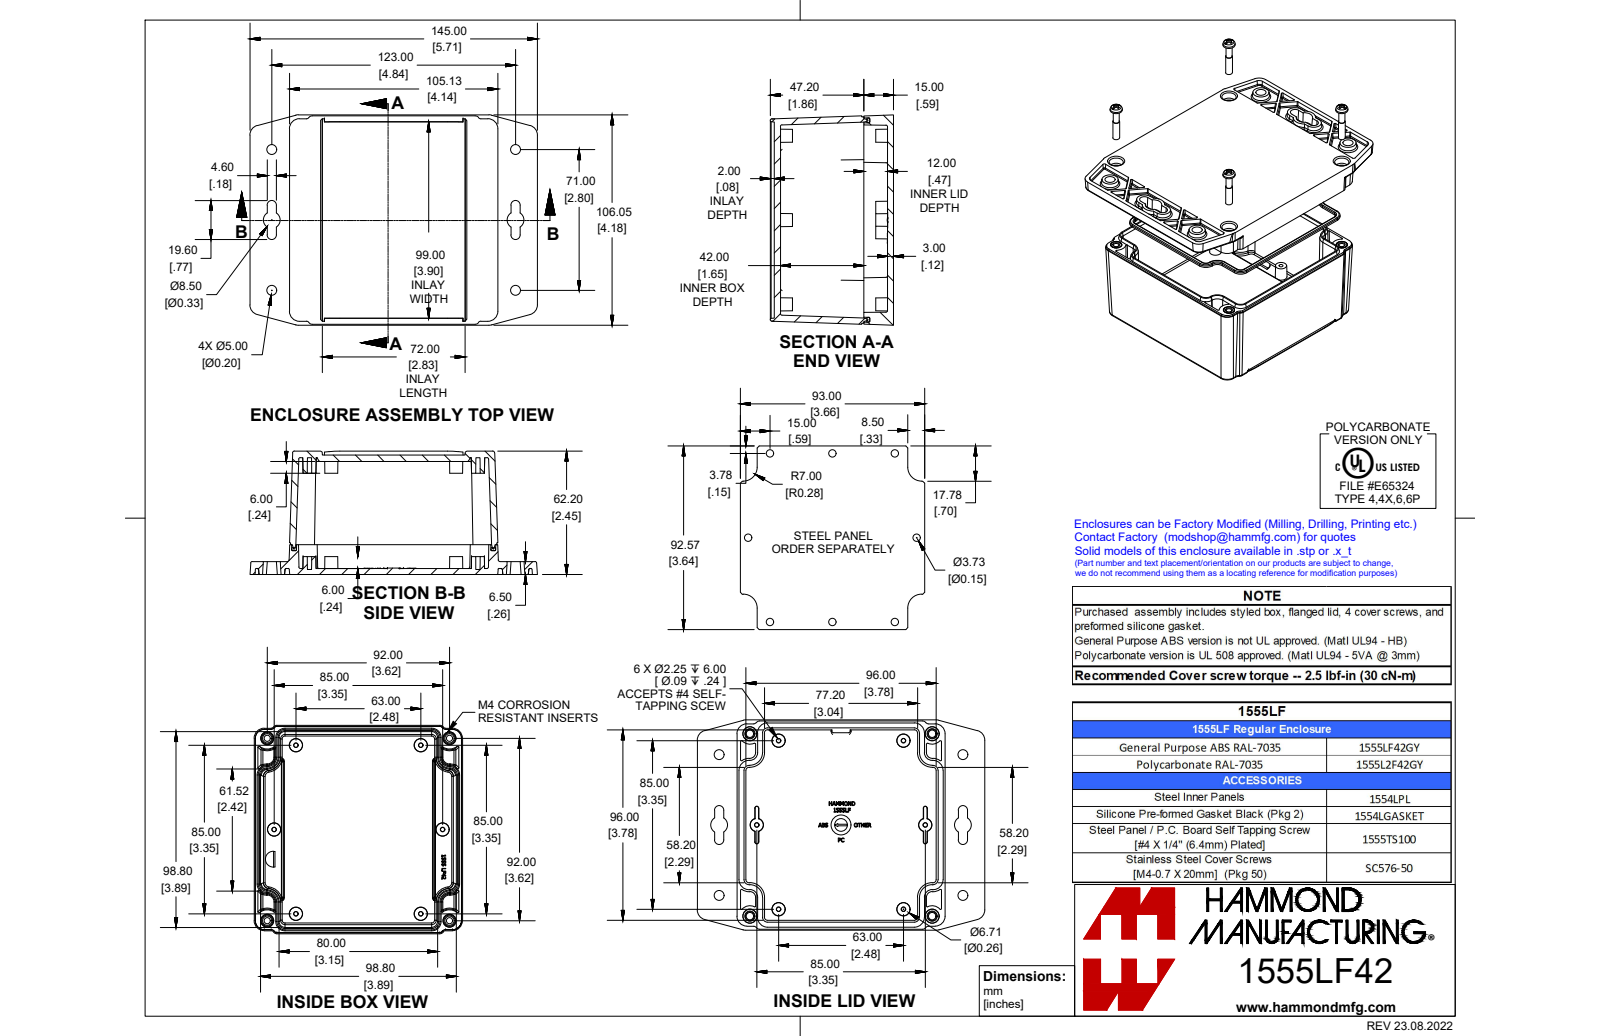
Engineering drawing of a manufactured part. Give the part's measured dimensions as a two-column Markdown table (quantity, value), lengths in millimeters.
| quantity | value |
| --- | --- |
| part name | 1555L2F42GY |
| STEP written by | SolidWorks 2021 (AUTOMOTIVE_DESIGN) |
| units | millimeters |
| bodies | 7 solids, 1311 faces (429 planar, 322 cylindrical, 560 other) |
| overall size | 145 × 106 × 62.2 |
| volume | 179 600 mm³ |
| surface area | 119 900 mm² |
| round holes (diameter × count) | 3.3 × 4, 4 × 4 |
| round bosses / shafts (diameter × count) | 7 × 4, 3.9 × 4, 3.5 × 4 |
| partial cylindrical surfaces (radius × count) | 0.5 × 112, 0.8 × 48, 0.3 × 16, 1 × 8, 2.6 × 8, 5 × 8, 5.1 × 8, 3 × 4 |
| main face-to-face distances | 3.2, 3, 57.2, 60.2, 54, 57, 3.1, 3.5, 6.5, 53.7 |
| hole center spacings | 92, 130.1 |
